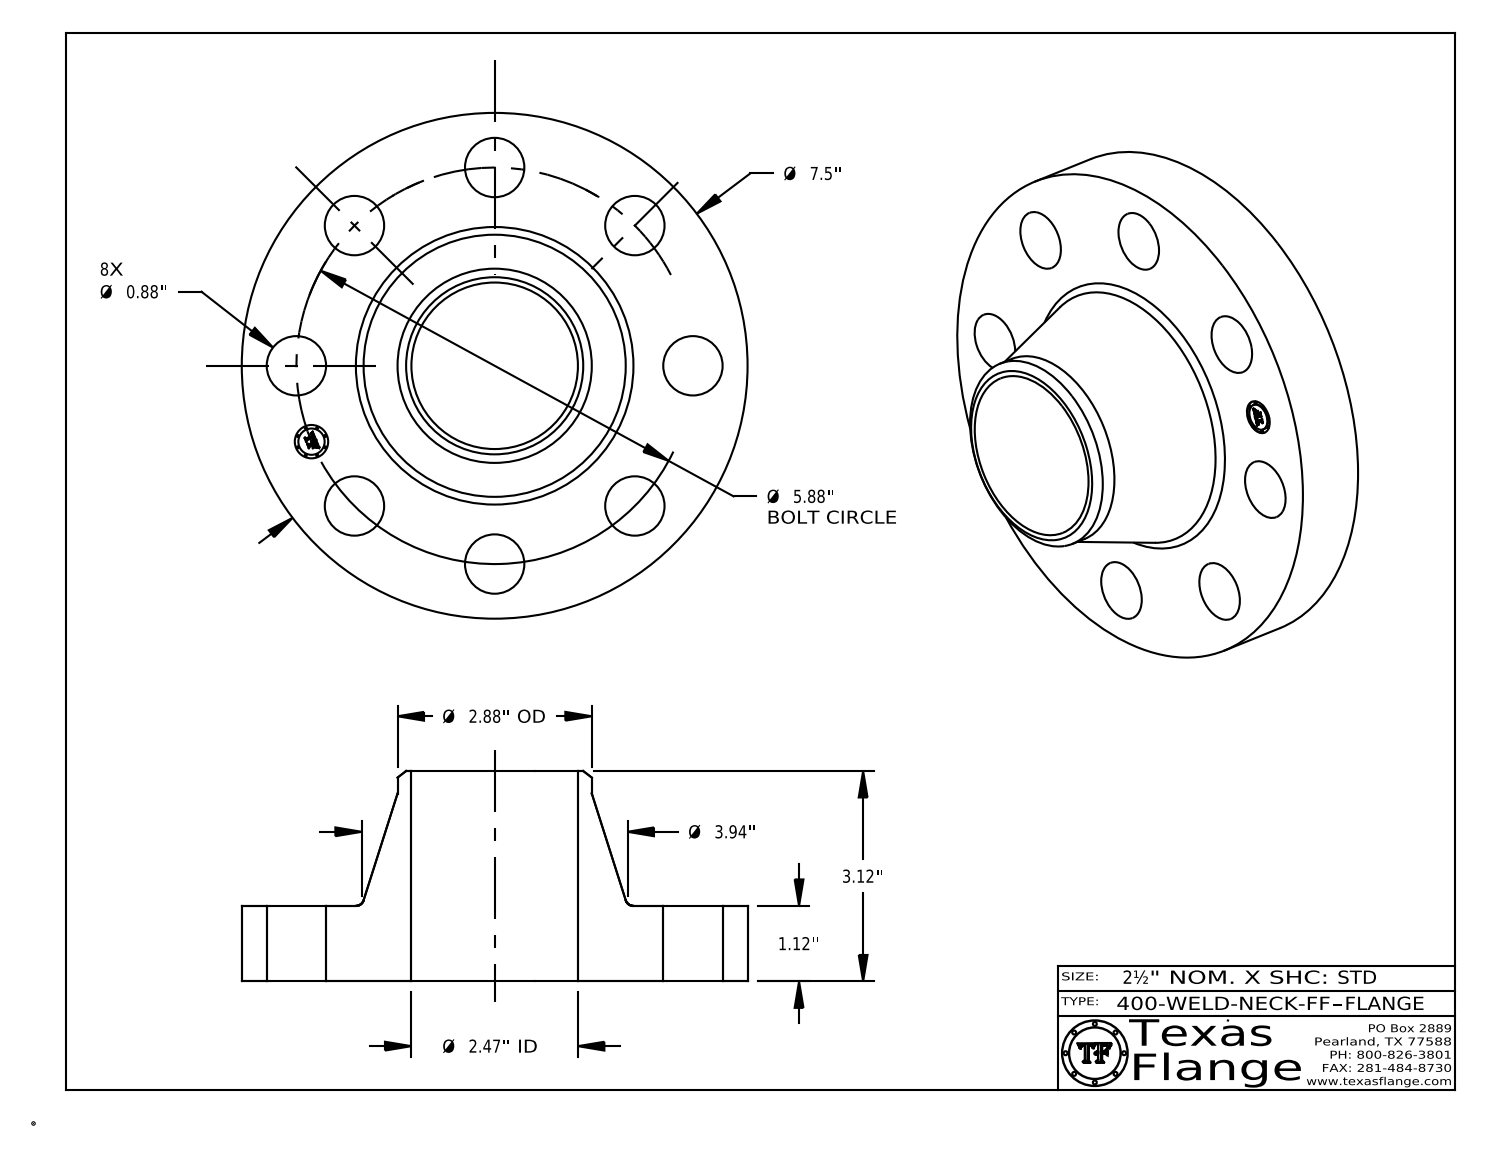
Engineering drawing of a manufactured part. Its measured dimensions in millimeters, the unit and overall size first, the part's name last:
Units: millimetres
Overall size (bounding box): 190.5 × 190.5 × 79.2
Round holes (diameter × count): ⌀22.4 ×8, ⌀12.6 ×1, ⌀62.7 ×1
Round bosses / shafts (diameter × count): ⌀0.8 ×8, ⌀190.5 ×1, ⌀73.2 ×1, ⌀9.9 ×1
Main face-to-face distances: 28.4, 79.2, 50.8, 0.4, 28.1, 51.2, 3.8, 3.7, 0.7, 2.4
Hole centre spacings: 57.2, 138, 74.7, 74.7, 105.6, 105.6, 83, 149.4
Volume: 763 100 mm³ · Surface area: 103 000 mm²
Bodies: 1 solid, 416 faces (368 planar, 42 cylindrical, 6 other)
Part name (STEP PRODUCT): 400-WELD-NECK-FF
STEP written by: CATIA V5 STEP AP214 (AUTOMOTIVE_DESIGN)
